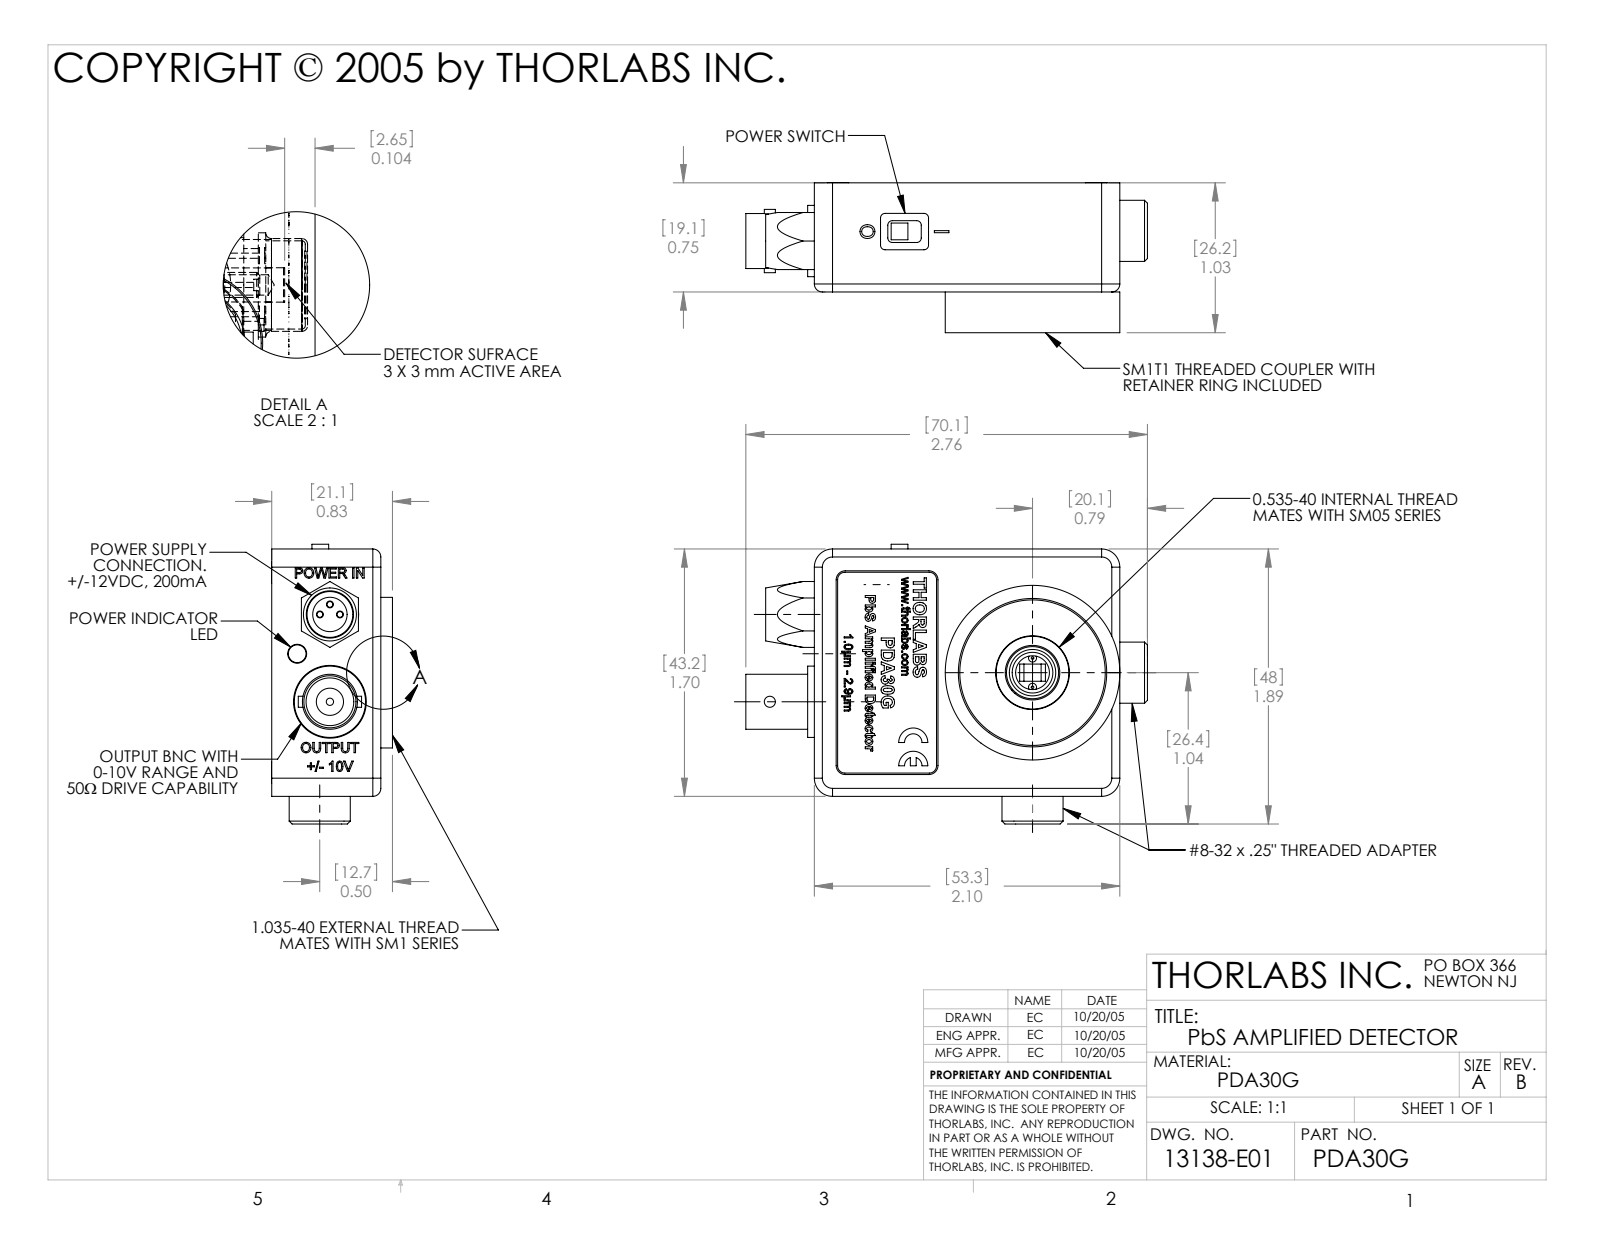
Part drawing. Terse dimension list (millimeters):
name: 13138-E0W
written by: SolidWorks 2009 (AUTOMOTIVE_DESIGN)
unit: mm
bodies: 17 solids, 1751 faces (936 planar, 271 cylindrical, 544 other)
size: 70.13 × 48.83 × 26.2
volume: 23 750 mm³; area: 26 858 mm²
holes: 7× ⌀1.78, 7× ⌀2.44, 4× ⌀3.17, 4× ⌀5.08, 3× ⌀0.71, 3× ⌀1, 2× ⌀1.4, 2× ⌀3.45, 2× ⌀3.81, 2× ⌀5, 1× ⌀1.27, 1× ⌀1.32
bosses: 4× ⌀3.73, 4× ⌀2.18, 3× ⌀0.45, 2× ⌀10.67, 2× ⌀5.99, 1× ⌀30.48, 1× ⌀26.29, 1× ⌀12.7
rounds: 22× R3.17, 12× R0.79, 8× R2.41, 4× R1.27, 4× R1.4, 4× R1.59, 3× R0.25, 2× R1.52
face distances: 1.59, 2.54, 13.08, 11.49, 1.27, 11.48, 9.89, 1.6, 1.78, 4.19
hole spacings: 3.6, 22.16, 1.75, 2.54, 37.1, 2.47, 2.55, 3.59
